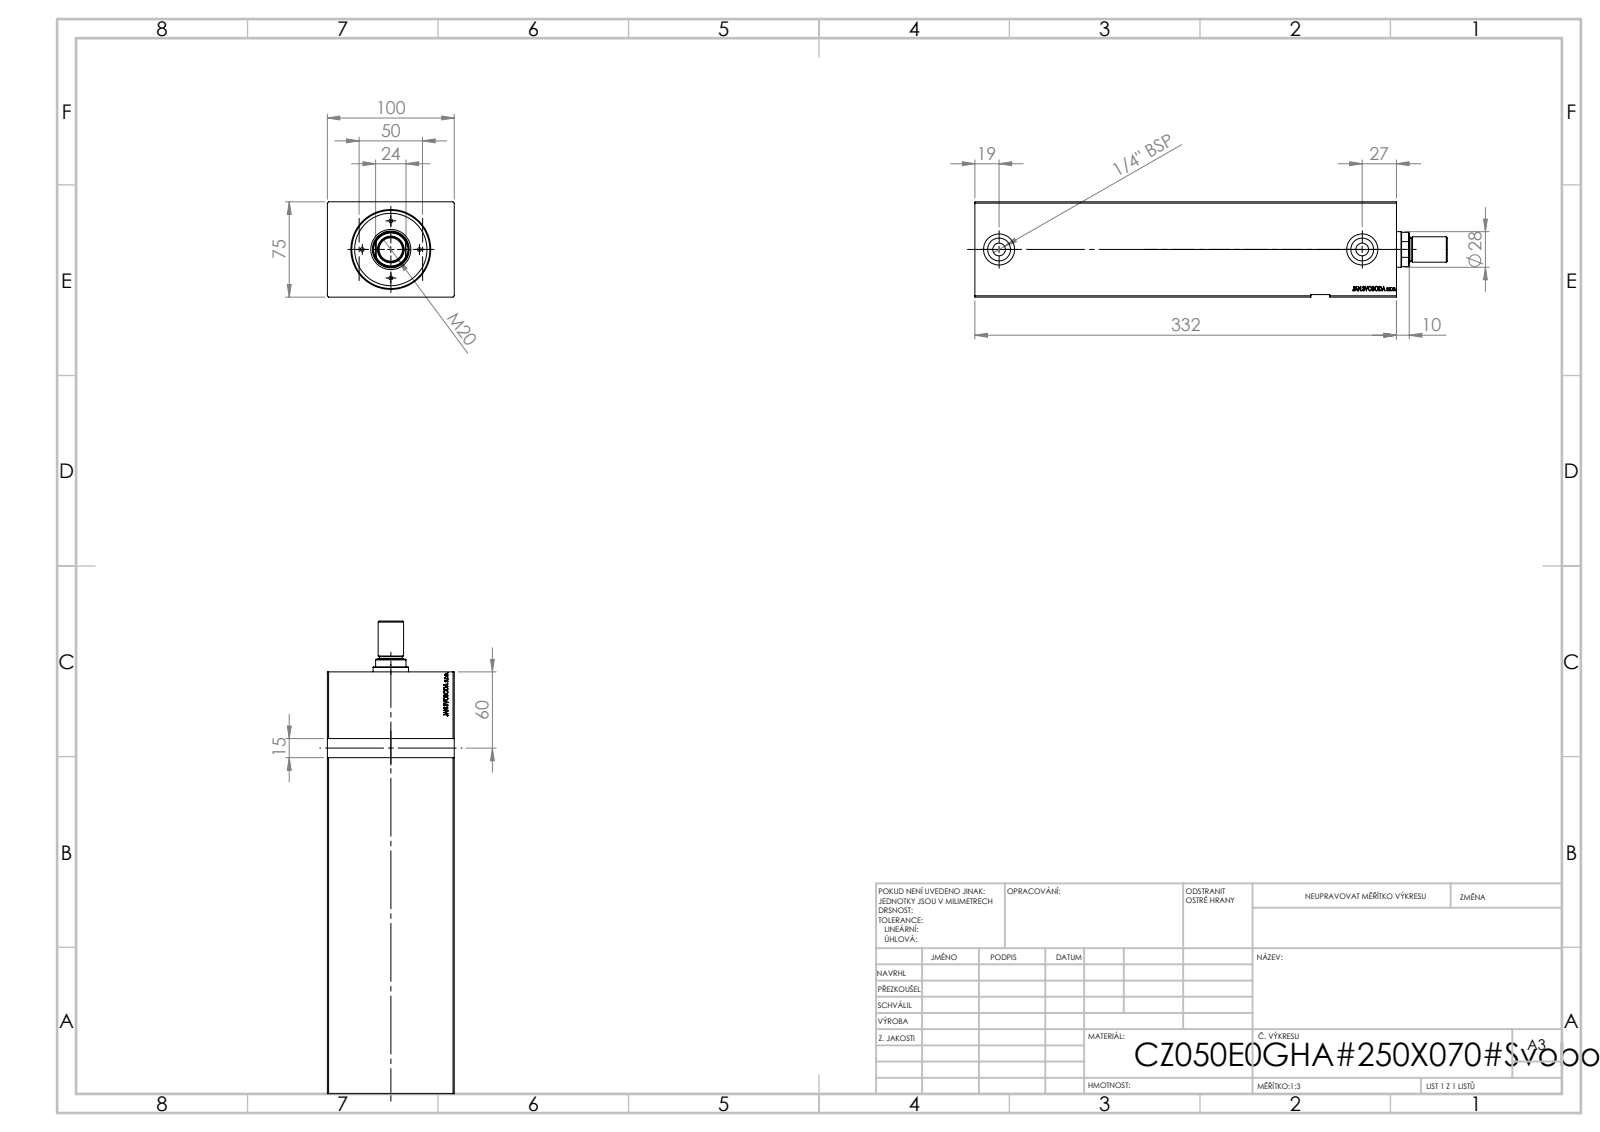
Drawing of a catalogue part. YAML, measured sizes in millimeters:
step_written_by: "SolidWorks 2019 (CONFIG_CONTROL_DESIGN)"
units: millimeters
bodies: {solids: 1, faces: 799, planar: 395, cylindrical: 22, other: 382}
overall_size: [332, 100, 75]
volume: 1851000
surface_area: 182644
round_holes:
  - {diameter: 8, count: 2}
  - {diameter: 10, count: 2}
  - {diameter: 18, count: 2}
  - {diameter: 24.5, count: 2}
  - {diameter: 36, count: 1}
  - {diameter: 50, count: 1}
  - {diameter: 61.5, count: 1}
face_to_face_distances: [75, 100, 332, 314.2, 17.8, 2, 73, 331.8, 17.6, 10]
hole_center_spacings: [266, 286]
